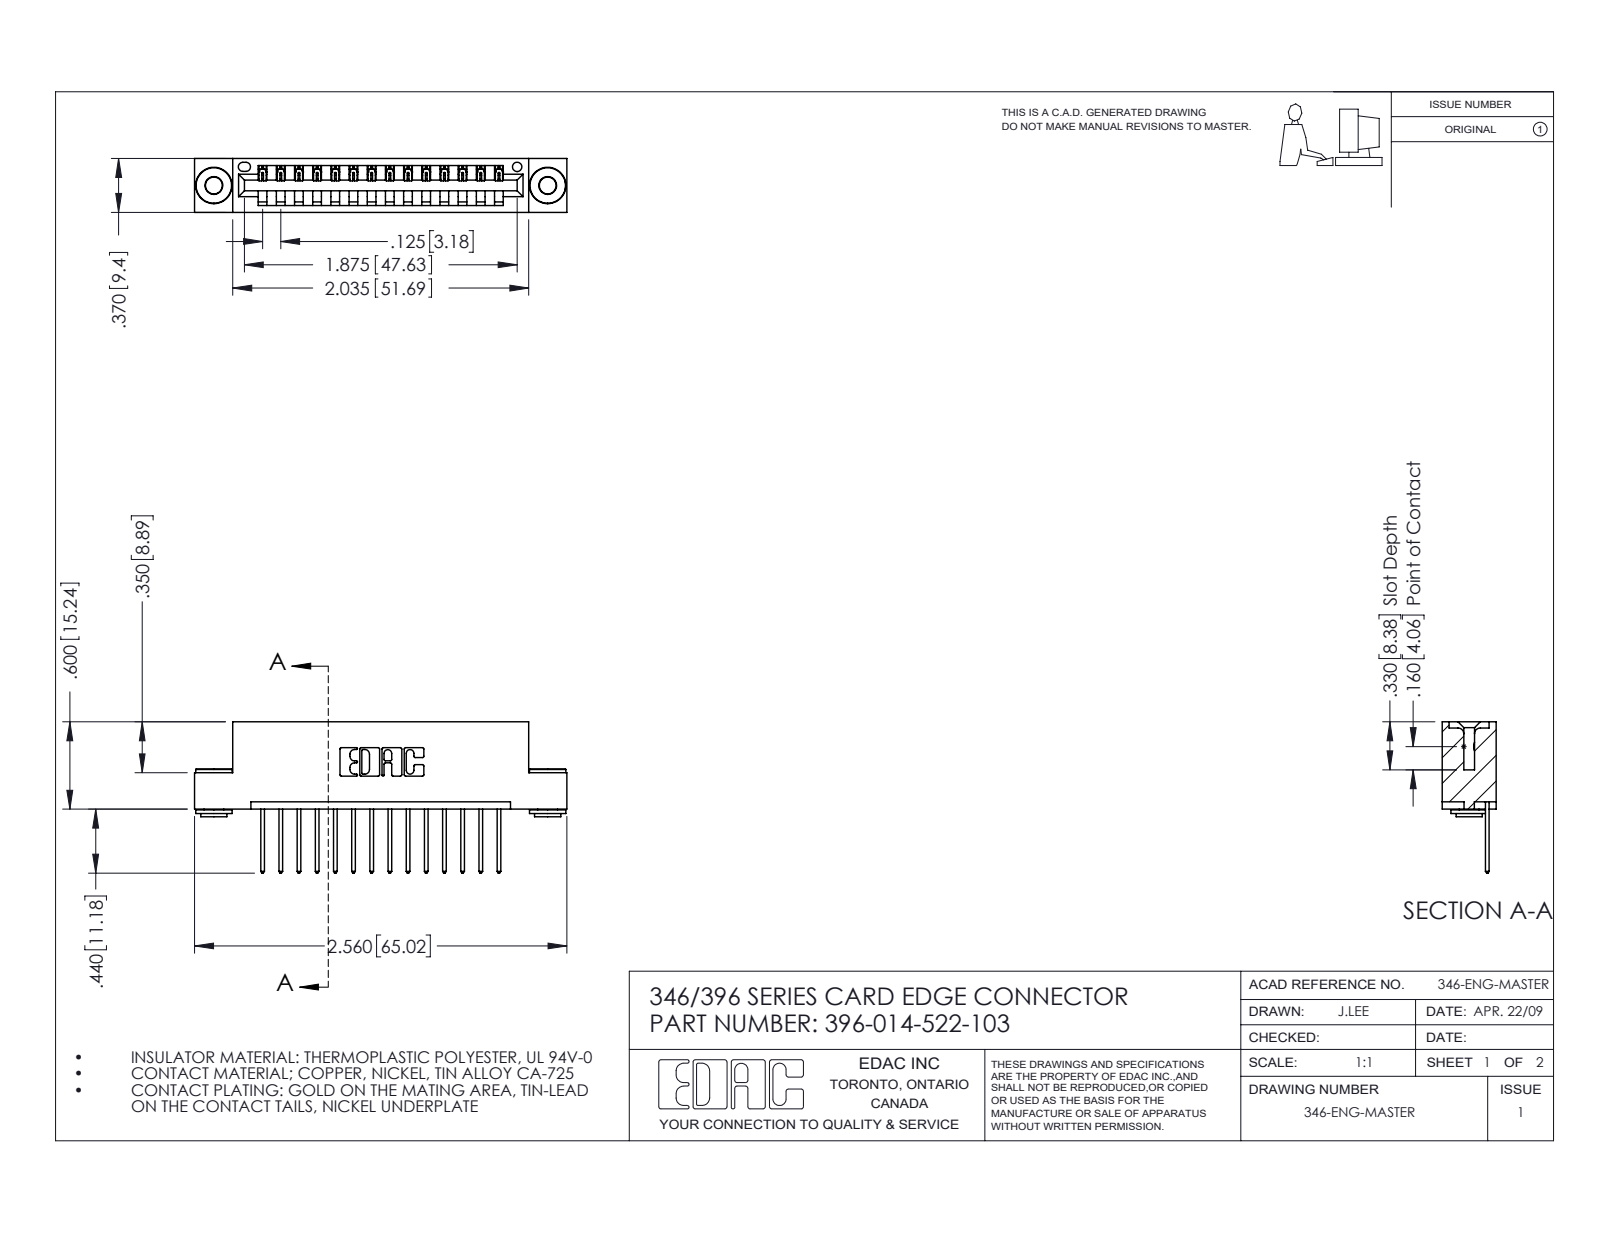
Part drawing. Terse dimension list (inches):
name: 346 Part_Flush Mounting Lugs - 0.156 Dia-TH; 345-292-001_345-293-122; 396-014-522-103; 345-250-002_345-250-002-102
written by: SolidWorks 2016 (CONFIG_CONTROL_DESIGN)
unit: in
bodies: 17 solids, 972 faces (646 planar, 318 cylindrical, 8 other)
size: 2.56 × 1.04 × 0.37
volume: 0.369 in³; area: 11.68 in²
holes: 2× ⌀0.116, 2× ⌀0.156, 1× ⌀0.064
bosses: 2× ⌀0.25, 2× ⌀0.18, 2× ⌀0.136
rounds: 28× R0.006, 28× R0.01, 22× R0.01, 6× R0.007, 6× R0.031, 3× R0.026, 2× R0.031, 2× R0.04
face distances: 0.25, 0.048, 0.322, 0.37, 0.025, 0.072, 0.298, 0.148, 0.222, 0.1
hole spacings: 0.246, 2.089, 2.295
